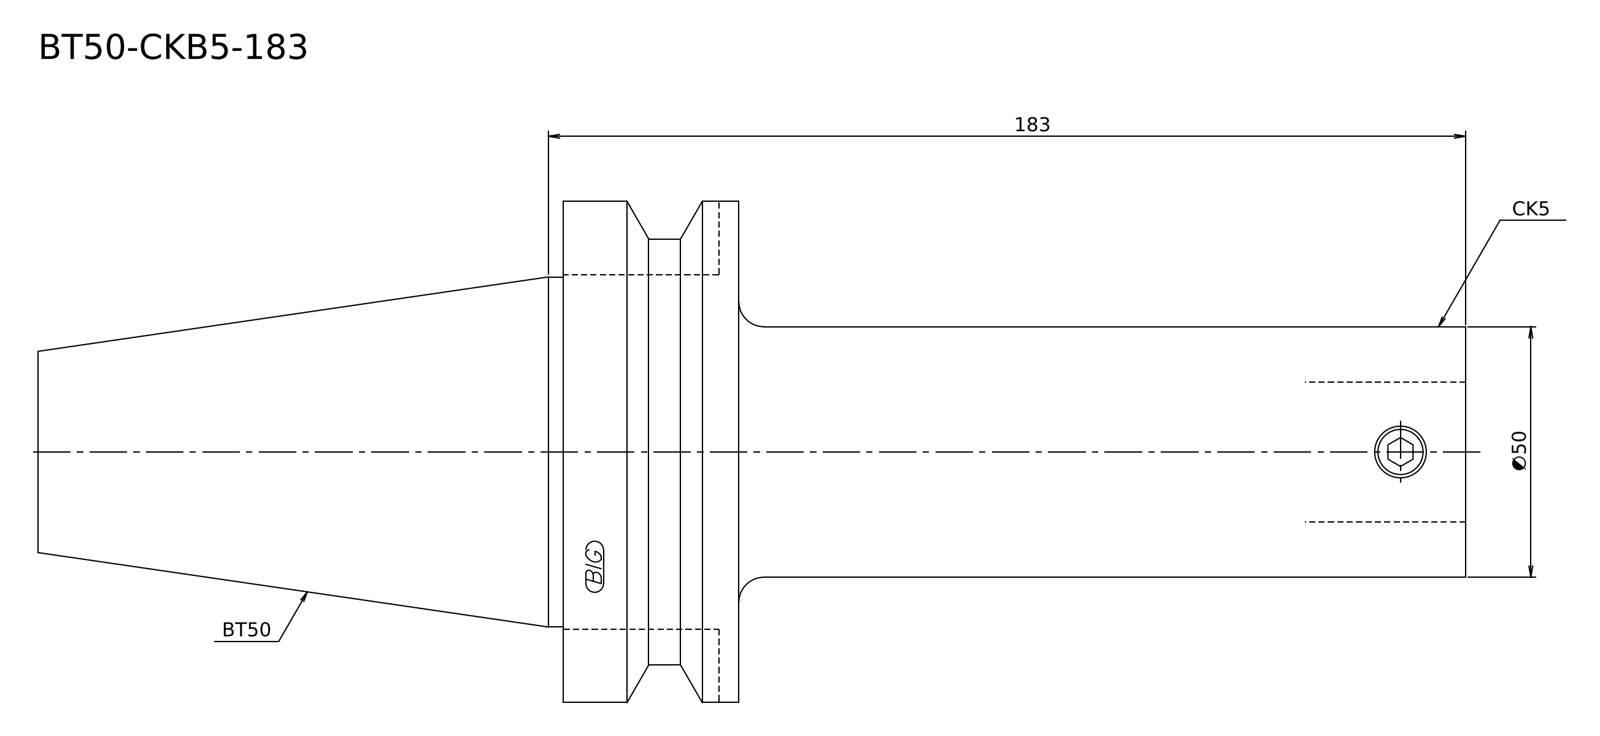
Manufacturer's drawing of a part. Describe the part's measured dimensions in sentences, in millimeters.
Its 3-D file was written by "Kubotek KeyCreator V8.5.1 (14335) (CONFIG_CONTROL_DESIGN)". It is 1 solid with 13 faces: 4 planar, 5 cylindrical and 4 other. Overall it measures 284.8 by 100 by 100 millimeters. Its volume is 797 447 cubic millimeters and its surface area 66 937 square millimeters. Round bosses or shafts: 1 of diameter 100, 1 of diameter 85, 1 of diameter 69.85, 1 of diameter 50. The main face-to-face distances are 35, 145, 180, 284.8, 139.8, 104.8.
